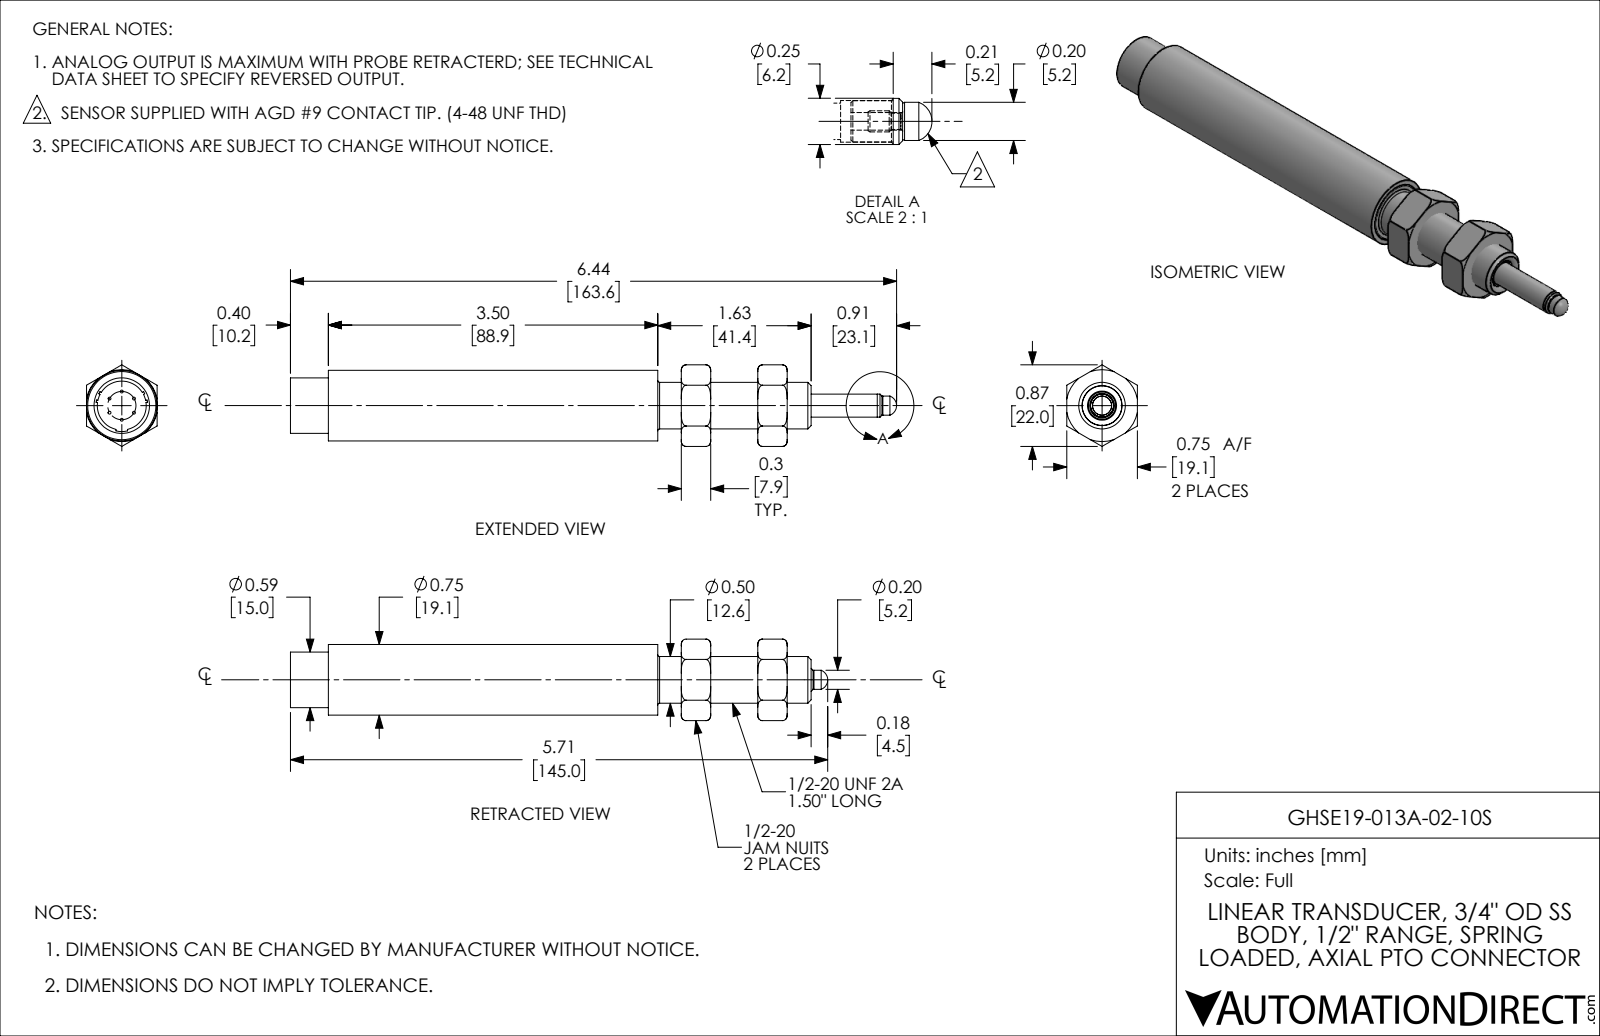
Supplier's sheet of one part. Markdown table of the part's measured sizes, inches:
| quantity | value |
| --- | --- |
| part name | GHSE19-013A-02-10S_retracted |
| STEP written by | SolidWorks 2019 (AUTOMOTIVE_DESIGN) |
| units | inches |
| bodies | 11 solids, 187 faces (77 planar, 65 cylindrical, 45 other) |
| overall size | 5.708 × 0.866 × 0.75 |
| volume | 1.194 in³ |
| surface area | 36.61 in² |
| round holes (diameter × count) | 0.093 × 1, 0.156 × 1, 0.193 × 1, 0.221 × 1, 0.249 × 1, 0.302 × 1, 0.31 × 1, 0.453 × 1, 0.52 × 1, 0.62 × 1, 0.625 × 1, 0.65 × 1 |
| round bosses / shafts (diameter × count) | 0.03 × 6, 0.75 × 1, 0.725 × 1, 0.672 × 1, 0.624 × 1, 0.59 × 1, 0.495 × 1, 0.375 × 1 |
| partial cylindrical surfaces (radius × count) | 0.011 × 2, 0.04 × 2, 0.133 × 1, 0.156 × 1, 0.275 × 1 |
| main face-to-face distances | 0.75, 0.812, 0.313, 0.813, 1.125, 0.5, 0.312, 0.75, 3.772, 4.085 |
